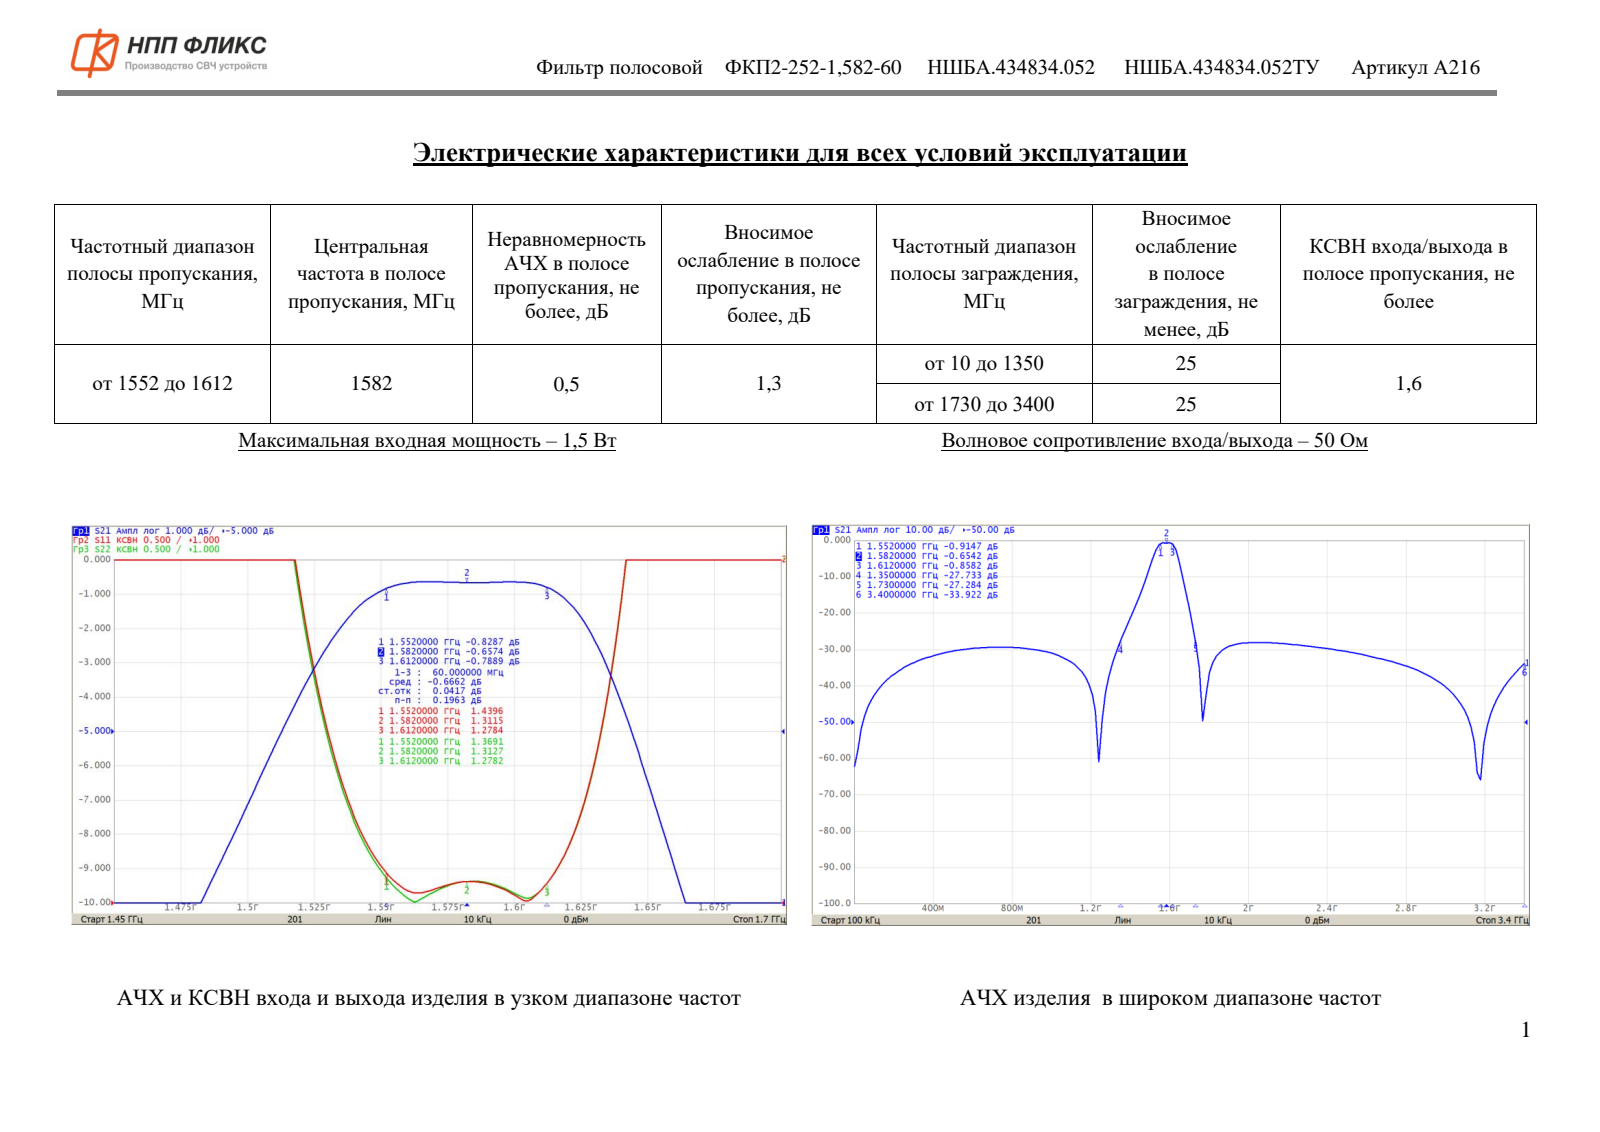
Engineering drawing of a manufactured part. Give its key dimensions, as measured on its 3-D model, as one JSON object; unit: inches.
{"part_name": "НШБА.434834.052_Фильтр ФКП2-252-1,582-60", "step_written_by": "ASCON Math Kernel (CONFIG_CONTROL_DESIGN)", "units": "inches", "bodies": {"solids": 1, "faces": 319, "planar": 213, "cylindrical": 11, "other": 95}, "overall_size": [0.39, 0.319, 0.174], "volume_in3": 0.014, "surface_area_in2": 0.558, "round_holes": [[0.039, 1]], "partial_cylinders_radius": [[0.008, 3], [0.012, 2], [0.004, 1], [0.014, 1], [0.024, 1]], "face_to_face_distances": [0.174, 0.02, 0.154, 0.28, 0.248, 0.339, 0.079, 0.091, 0.327, 0.142]}
